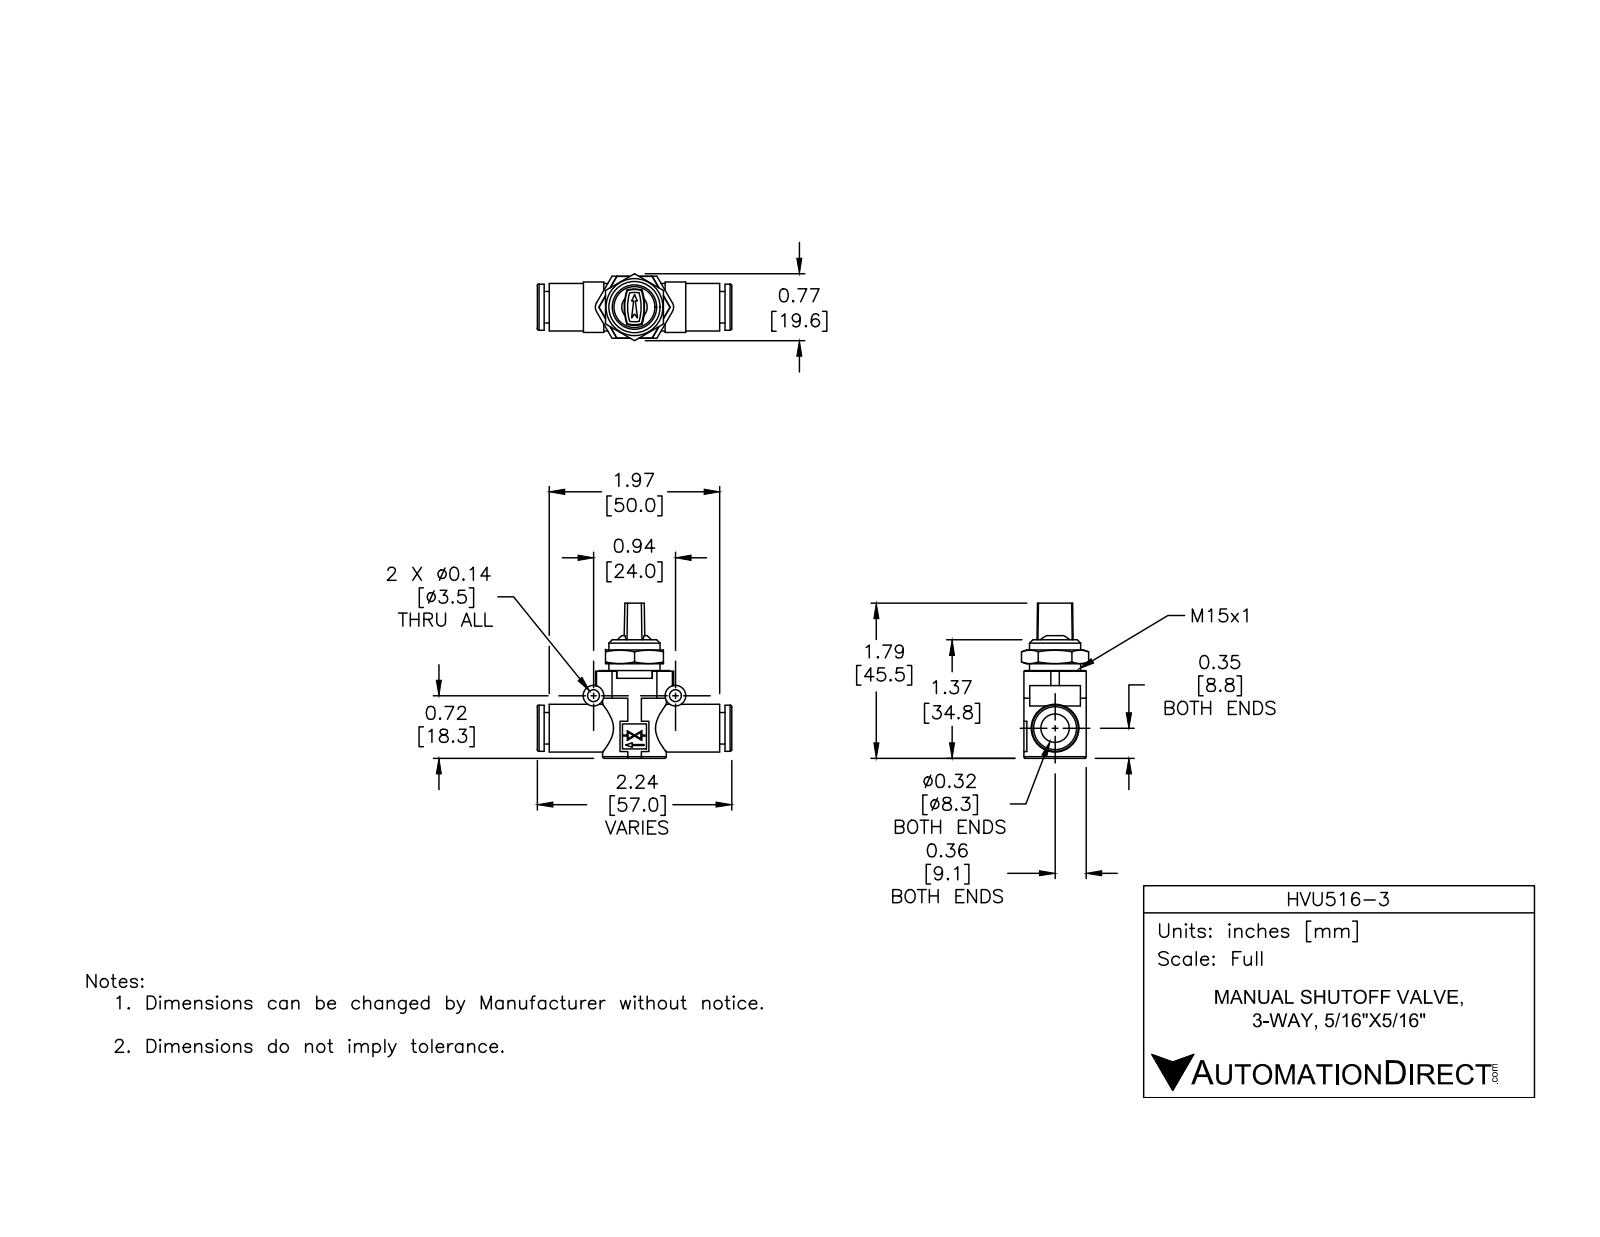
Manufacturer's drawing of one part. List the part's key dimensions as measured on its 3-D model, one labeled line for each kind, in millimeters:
Part name (STEP PRODUCT): HVU516-3
STEP written by: SolidWorks 2015 (CONFIG_CONTROL_DESIGN)
Units: millimetres
Bodies: 4 solids, 172 faces (105 planar, 47 cylindrical, 20 other)
Overall size (bounding box): 57 × 45.5 × 19.63
Volume: 13 788 mm³ · Surface area: 8 787 mm²
Round holes (diameter × count): ⌀3.5 ×2, ⌀8.25 ×1, ⌀9.5 ×1, ⌀12 ×1
Round bosses / shafts (diameter × count): ⌀6 ×2, ⌀18.65 ×1, ⌀15 ×1, ⌀14 ×1, ⌀13.55 ×1, ⌀9.25 ×1
Partial cylindrical surfaces — rounded edges, fillets, slot ends (radius × count): R0.5 ×2, R2.5 ×2, R7.03 ×2, R14.56 ×2
Main face-to-face distances: 23.49, 2, 1.5, 51.5, 18, 3.5, 53.5, 55, 18.22, 20.5
Hole centre spacings: 24
